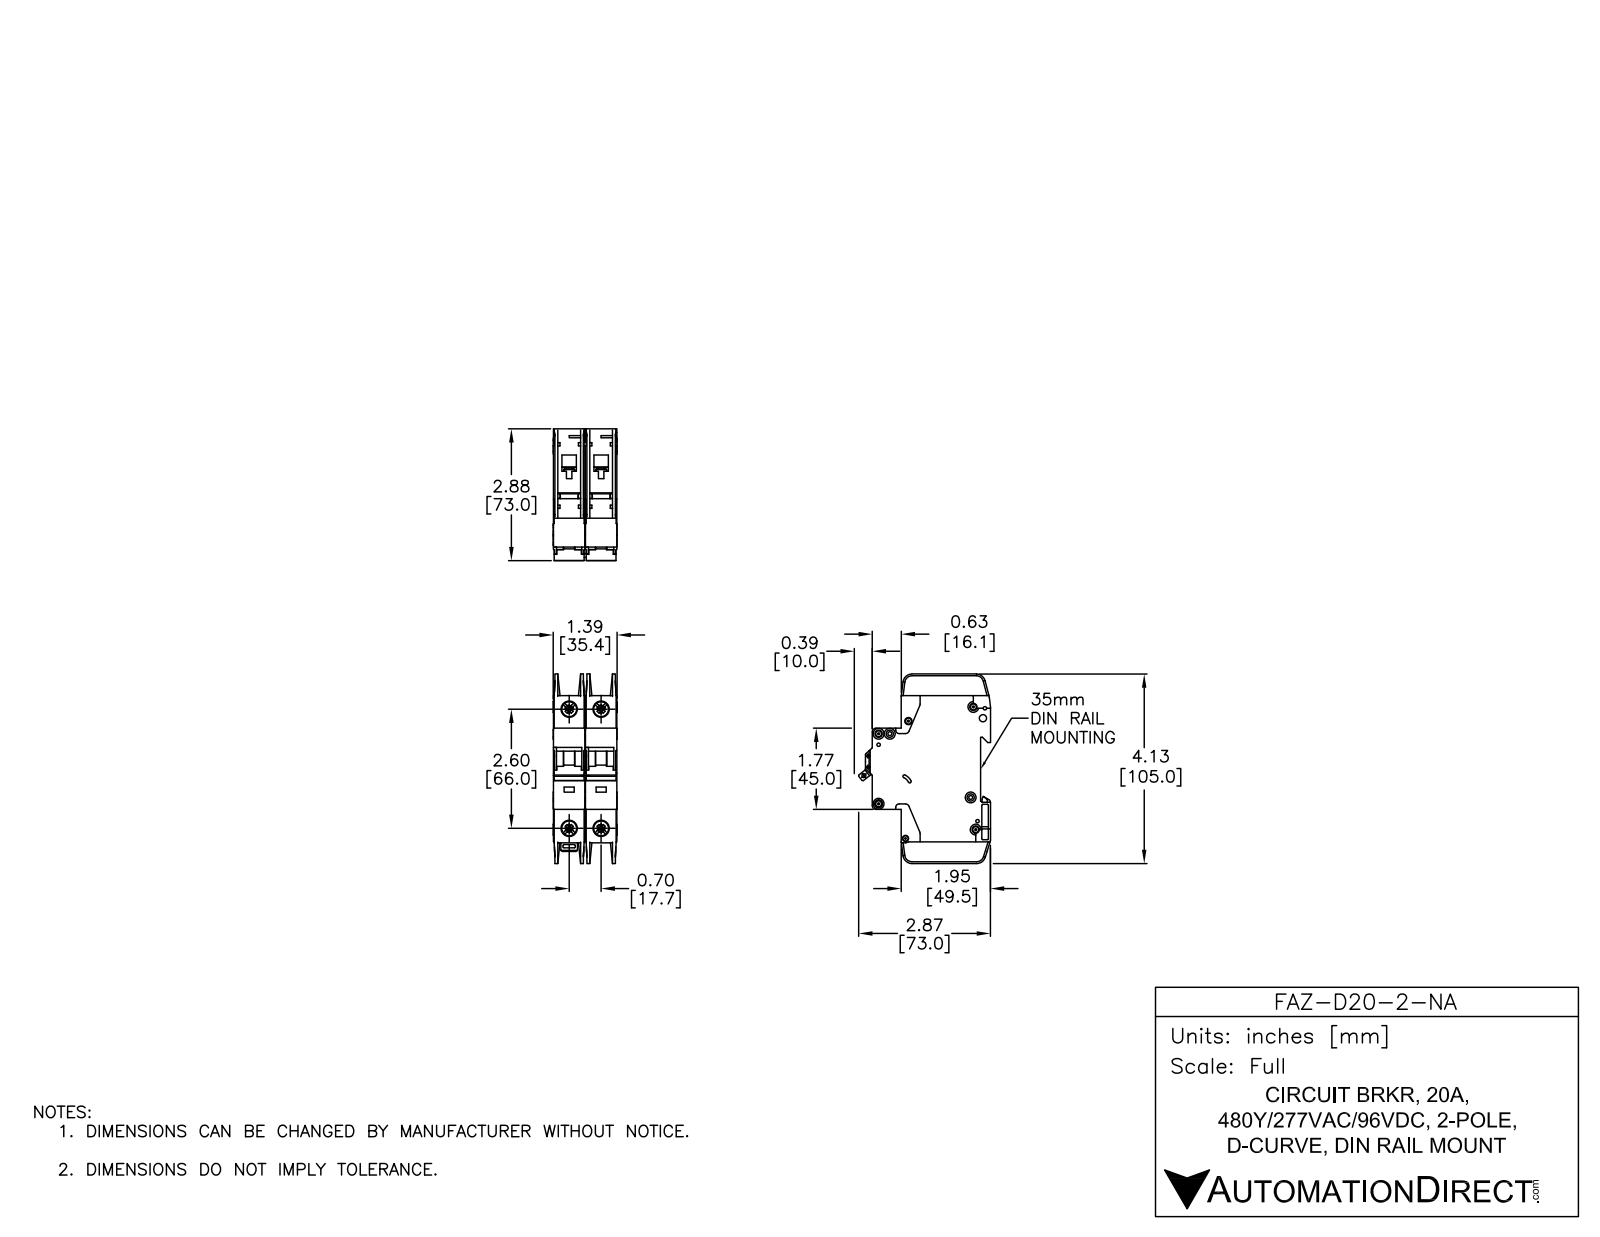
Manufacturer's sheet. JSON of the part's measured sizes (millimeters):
{"part_name": "FAZ-D20-2-NA", "step_written_by": "SolidWorks 2014 (AUTOMOTIVE_DESIGN)", "units": "millimeters", "bodies": {"solids": 6, "faces": 1568, "planar": 818, "cylindrical": 526, "other": 224}, "overall_size": [105, 73.04, 35.4], "volume_mm3": 155390, "surface_area_mm2": 49479, "round_holes": [[3.6, 7], [7.15, 4], [8.2, 4], [1.09, 2], [1.5, 2], [4, 2], [1.9, 1], [2.15, 1], [2.2, 1], [2.55, 1], [3.3, 1], [3.4, 1]], "round_bosses_or_shafts": [[6, 7], [2.5, 2]], "partial_cylinders_radius": [[0.25, 47], [0.5, 24], [1, 18], [2, 12], [5, 5], [1.8, 4], [4, 4], [0.2, 2]], "face_to_face_distances": [17.7, 17.5, 0.7, 15.05, 2.45, 1.75, 15.75, 13.3, 35.2, 17], "hole_center_spacings": [6.2, 17.7, 66, 68.33, 5.19, 6.1, 8.19, 8.56]}
